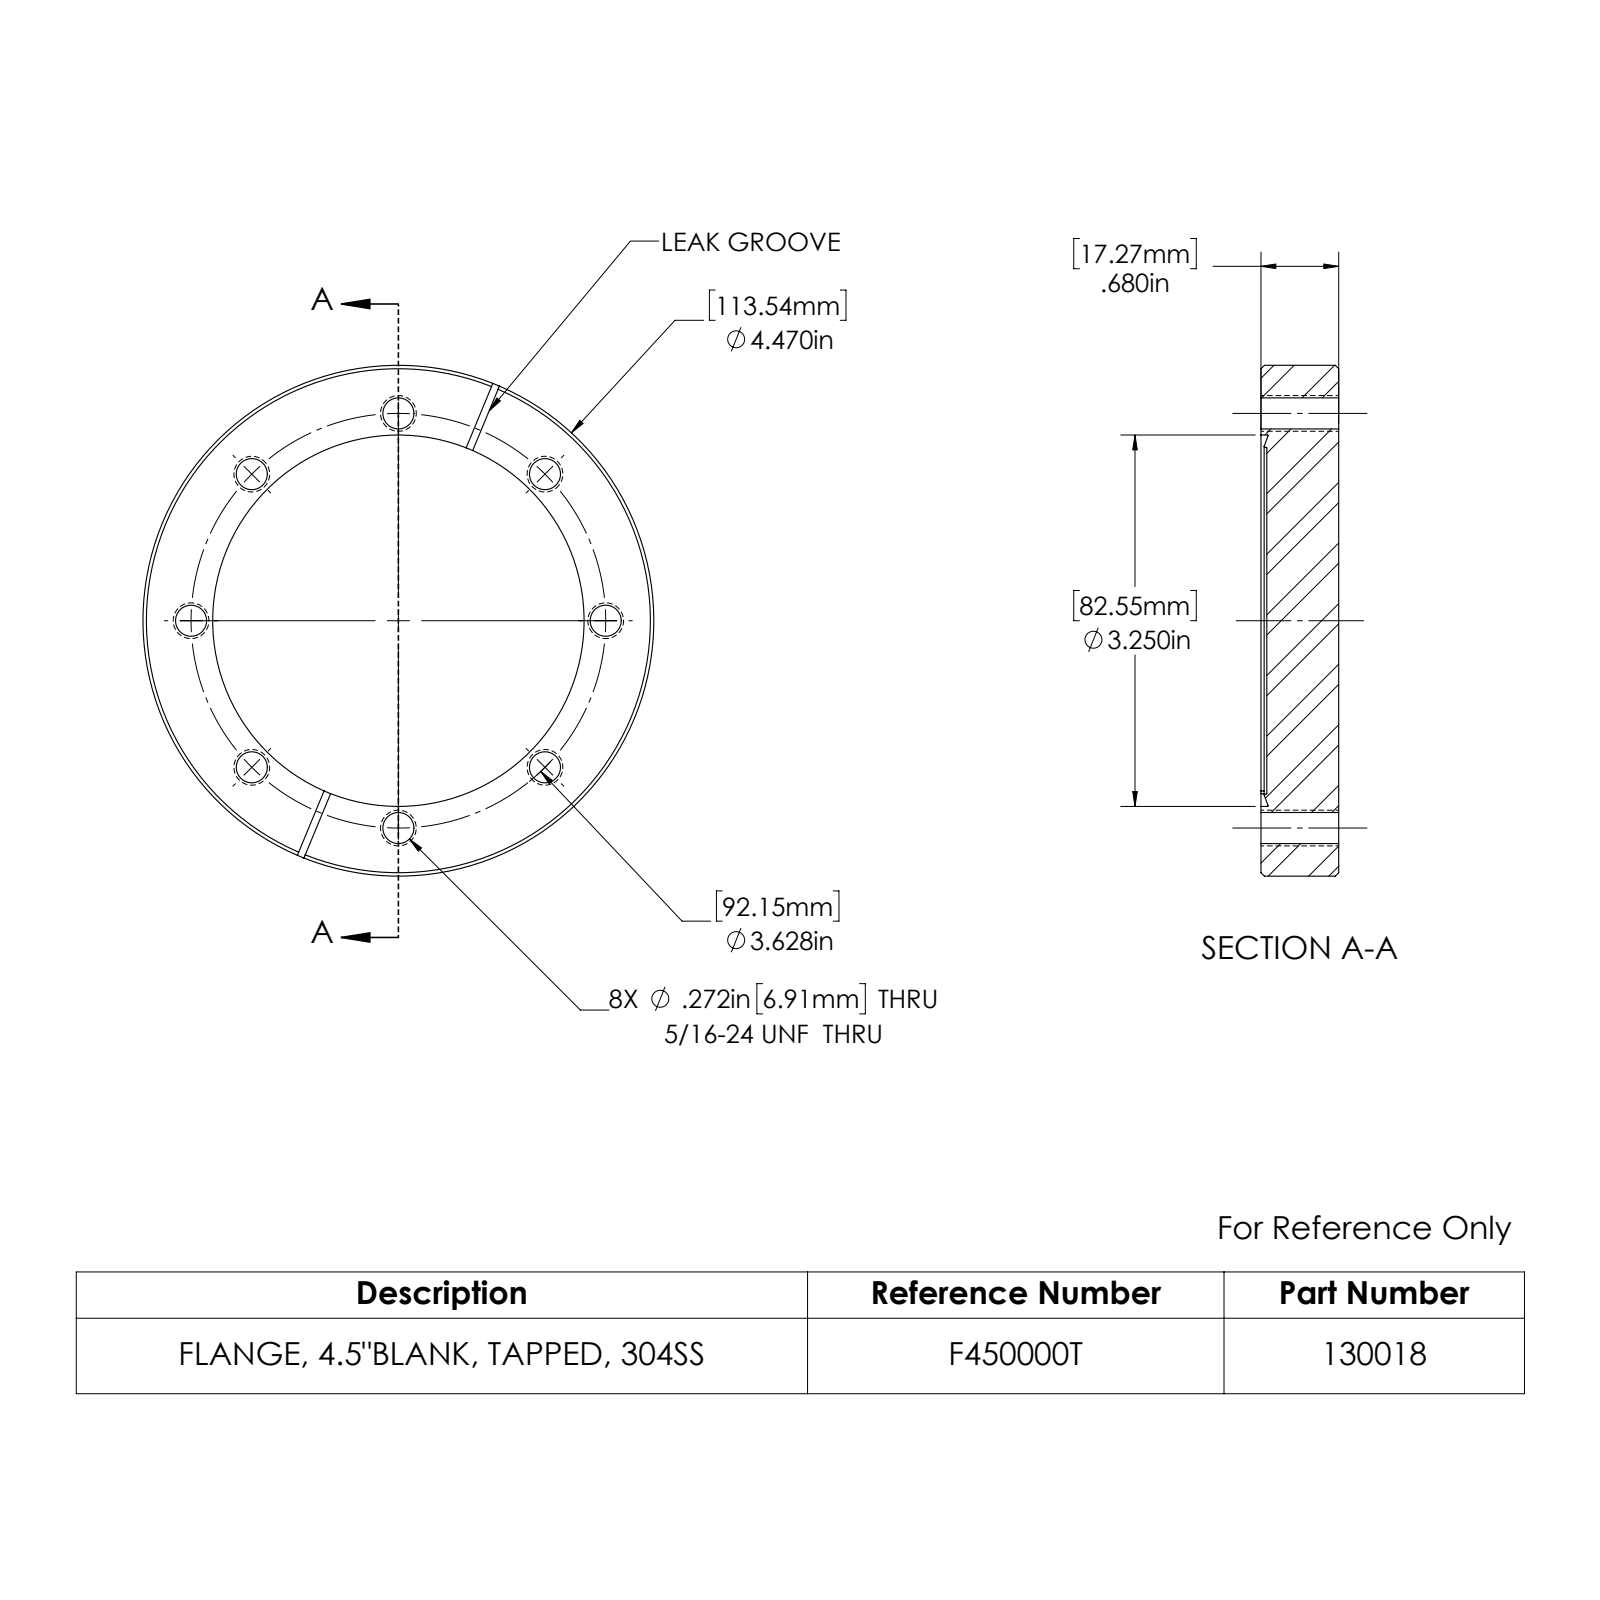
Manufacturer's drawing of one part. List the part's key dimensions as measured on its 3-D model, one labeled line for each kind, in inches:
Part name (STEP PRODUCT): 130018_D
STEP written by: SolidWorks 2022 (CONFIG_CONTROL_DESIGN)
Units: inches
Bodies: 1 solid, 45 faces (10 planar, 20 cylindrical, 15 other)
Overall size (bounding box): 4.47 × 4.47 × 0.68
Volume: 9.922 in³ · Surface area: 45.1 in²
Round holes (diameter × count): ⌀0.272 ×8, ⌀3.25 ×1
Round bosses / shafts (diameter × count): ⌀4.47 ×1
Main face-to-face distances: 0.629, 0.051, 0.68, 0.052, 0.628, 0.062, 0.061, 0.063, 0.062
Hole centre spacings: 1.389, 1.814, 3.352, 2.565, 2.566, 3.628, 3.628
